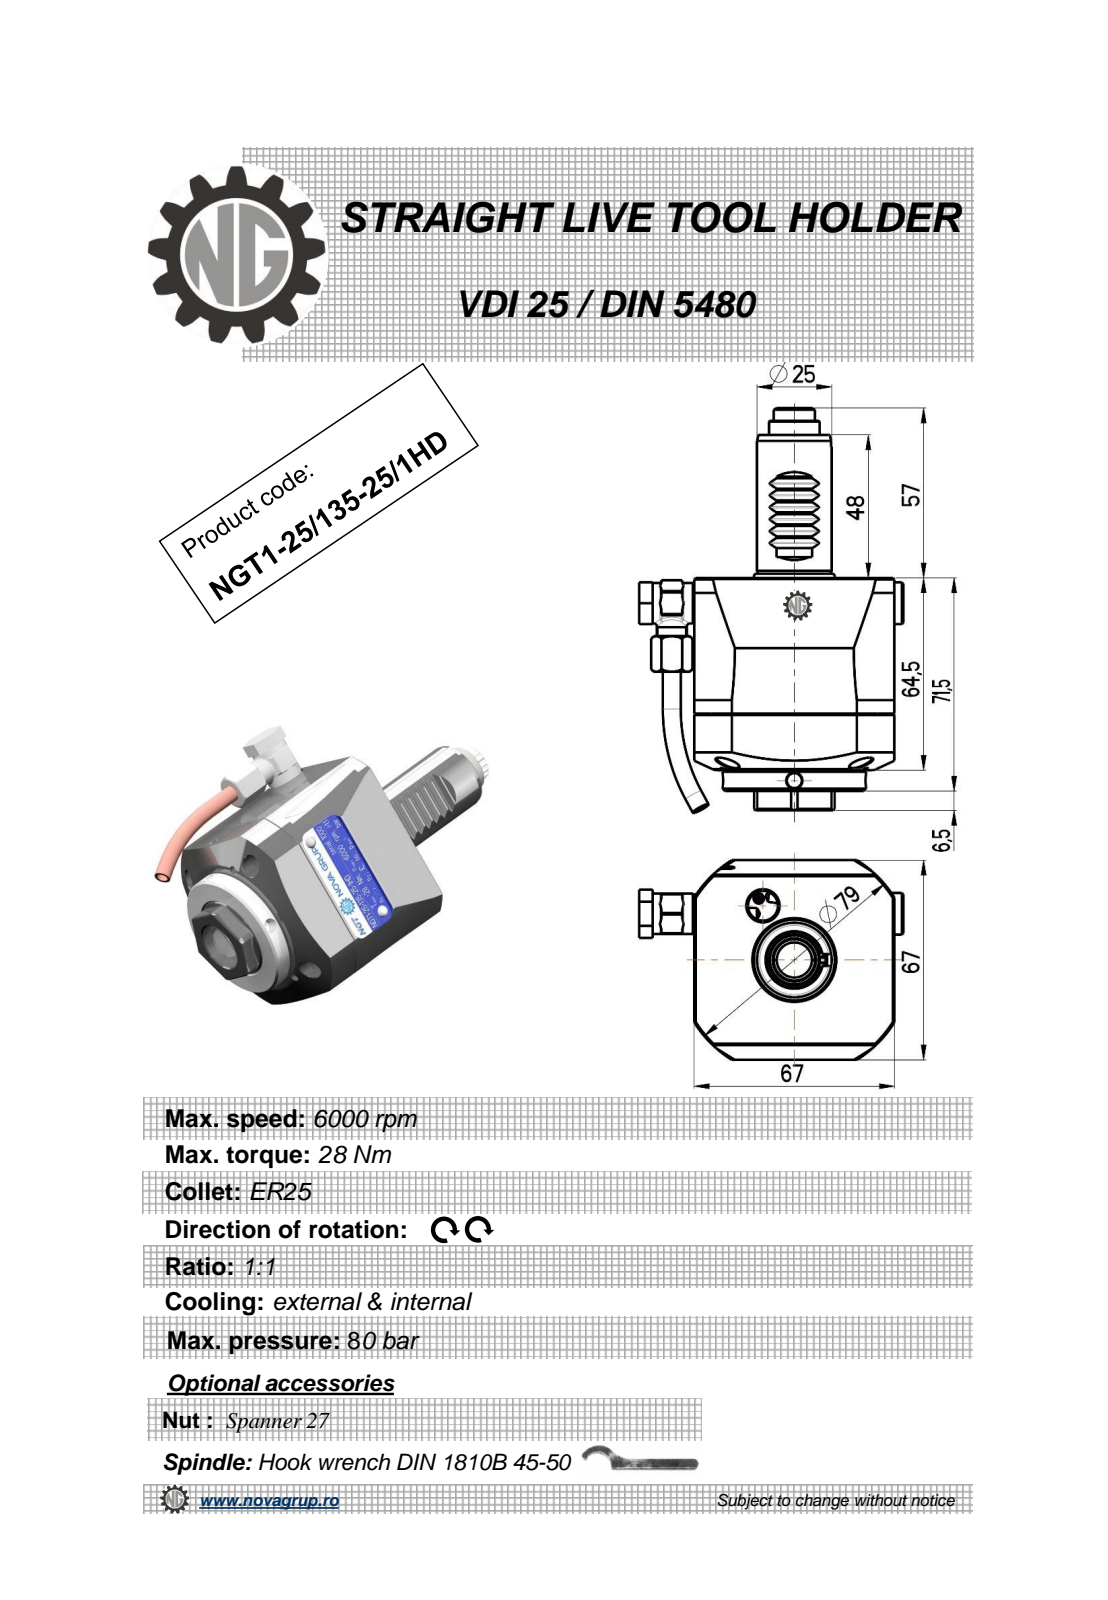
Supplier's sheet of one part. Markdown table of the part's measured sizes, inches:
| quantity | value |
| --- | --- |
| part name | NGT1_25_135_25_1HD |
| STEP written by | PRO/ENGINEER BY PARAMETRIC TECHNOLOGY CORPORATION, 2010280 (CONFIG_CONTROL_DESIGN) |
| units | inches |
| bodies | 1 solid, 429 faces (124 planar, 161 cylindrical, 144 other) |
| overall size | 5.348 × 3.48 × 2.638 |
| volume | 18.4 in³ |
| surface area | 54.21 in² |
| round holes (diameter × count) | 0.157 × 3, 0.197 × 2, 0.008 × 1, 0.118 × 1, 0.244 × 1, 0.354 × 1, 0.394 × 1, 0.433 × 1, 0.709 × 1, 1.043 × 1 |
| round bosses / shafts (diameter × count) | 0.236 × 2, 1.89 × 1, 0.984 × 1, 0.669 × 1, 0.551 × 1, 0.535 × 1, 0.512 × 1, 0.394 × 1 |
| partial cylindrical surfaces (radius × count) | 0.075 × 32, 0.012 × 6, 0.02 × 4, 0.239 × 1, 0.272 × 1, 0.303 × 1, 0.413 × 1, 0.591 × 1 |
| main face-to-face distances | 2.638, 2.815, 0.276, 2.539, 0.531, 0.472, 0.256, 3.071, 0.111, 1.063 |
| hole center spacings | 0.016, 1.726, 1.741, 2.421 |
